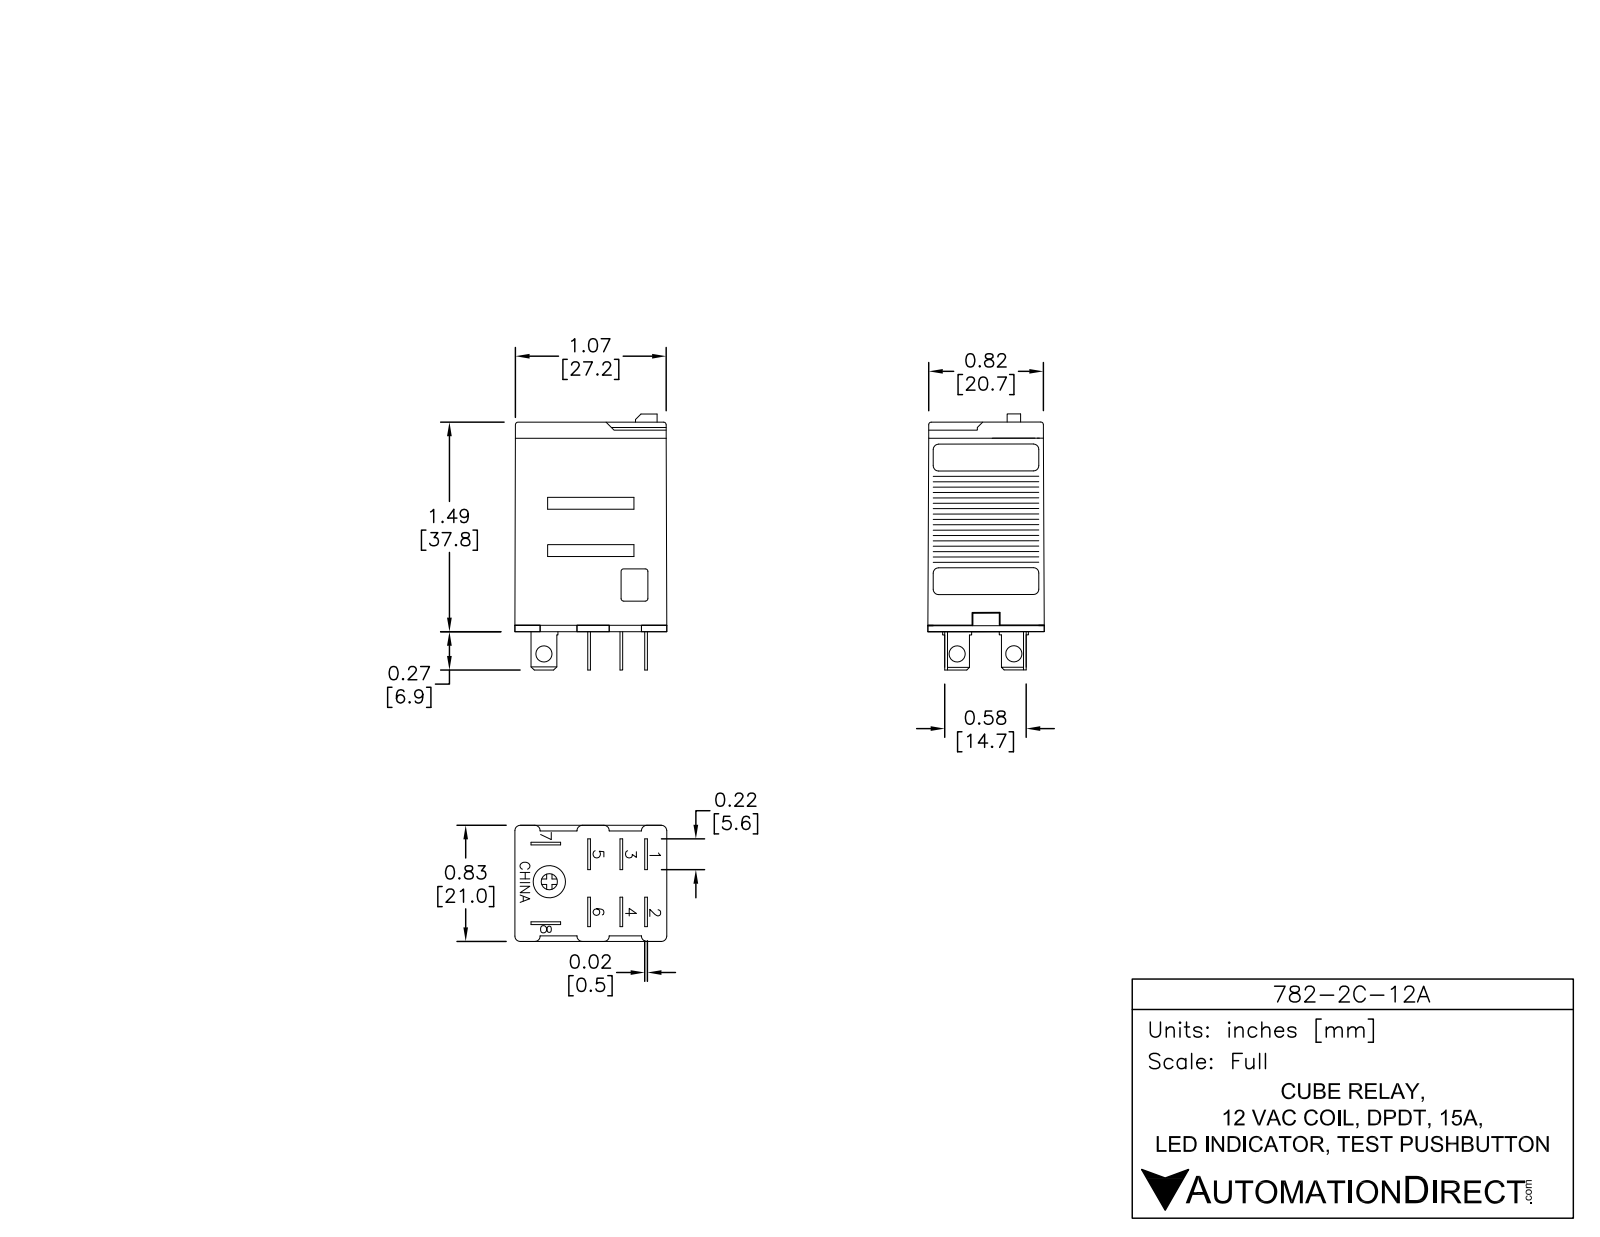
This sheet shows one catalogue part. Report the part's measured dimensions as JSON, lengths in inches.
{"part_name": "782-2C-12A", "step_written_by": "SolidWorks 2021 (CONFIG_CONTROL_DESIGN)", "units": "inches", "bodies": {"solids": 1, "faces": 197, "planar": 176, "cylindrical": 21, "other": 0}, "overall_size": [1.83, 1.1, 0.83], "volume_in3": 1.401, "surface_area_in2": 8.801, "round_holes": [[0.11, 3], [0.085, 1]], "round_bosses_or_shafts": [[0.07, 1]], "partial_cylinders_radius": [[0.24, 1]], "face_to_face_distances": [0.83, 1.1, 1.54, 0.02, 0.232, 0.03, 0.04, 1.53, 1.5, 0.185], "hole_center_spacings": [0.45]}
